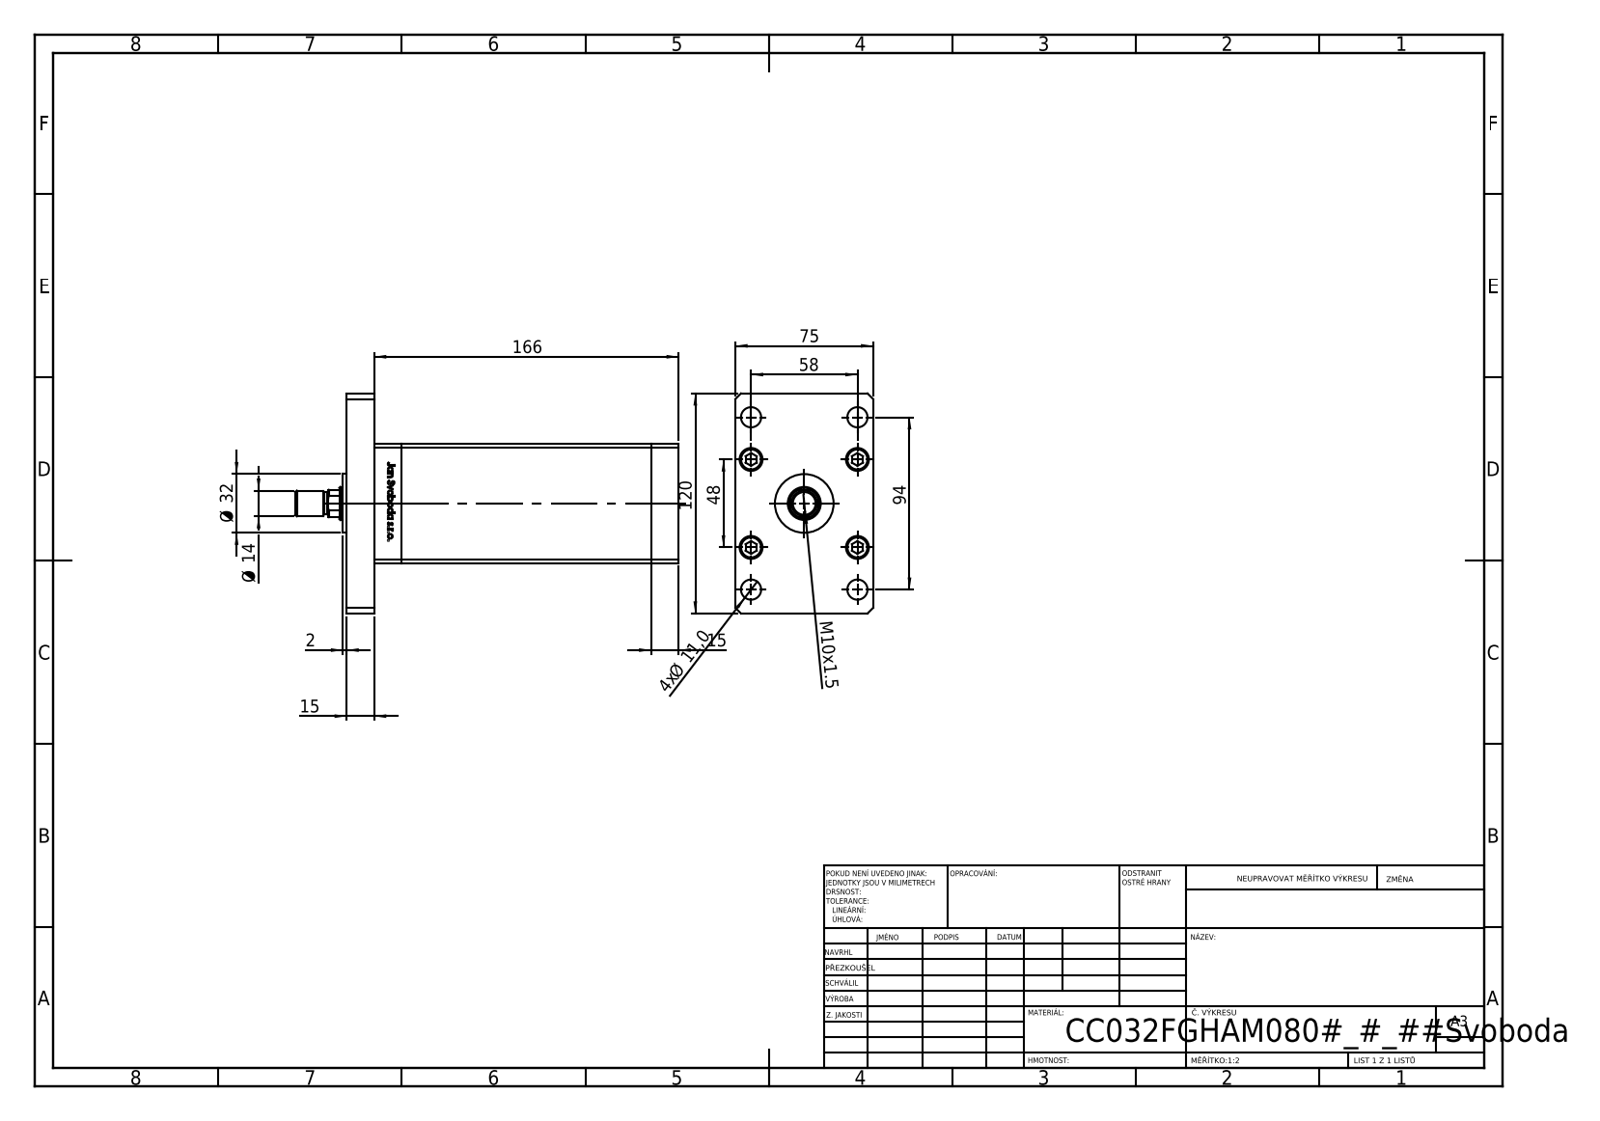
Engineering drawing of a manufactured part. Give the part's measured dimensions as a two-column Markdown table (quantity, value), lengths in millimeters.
| quantity | value |
| --- | --- |
| part name | V220C_F; V220CC_MALE_METRIC; V220C_FRONT_F; V220C BACK_F (+3 more) |
| STEP written by | SolidWorks 2019 (CONFIG_CONTROL_DESIGN) |
| units | millimeters |
| bodies | 20 solids, 1321 faces (518 planar, 191 cylindrical, 612 other) |
| overall size | 209 × 120 × 75 |
| volume | 851 216 mm³ |
| surface area | 161 029 mm² |
| round holes (diameter × count) | 9 × 5, 13.5 × 5, 8 × 4, 11 × 4, 12.5 × 4, 2 × 2, 13.16 × 2, 8.5 × 1, 18 × 1, 19.5 × 1 |
| round bosses / shafts (diameter × count) | 12.5 × 5, 8 × 5, 32 × 1, 14 × 1, 12 × 1 |
| partial cylindrical surfaces (radius × count) | 0.93 × 2, 8.5 × 1 |
| main face-to-face distances | 15, 75, 151, 166, 65, 30, 136, 181, 13, 153 |
| hole center spacings | 24, 23, 37.64, 55.23, 58, 62.39, 71, 91.68 |
